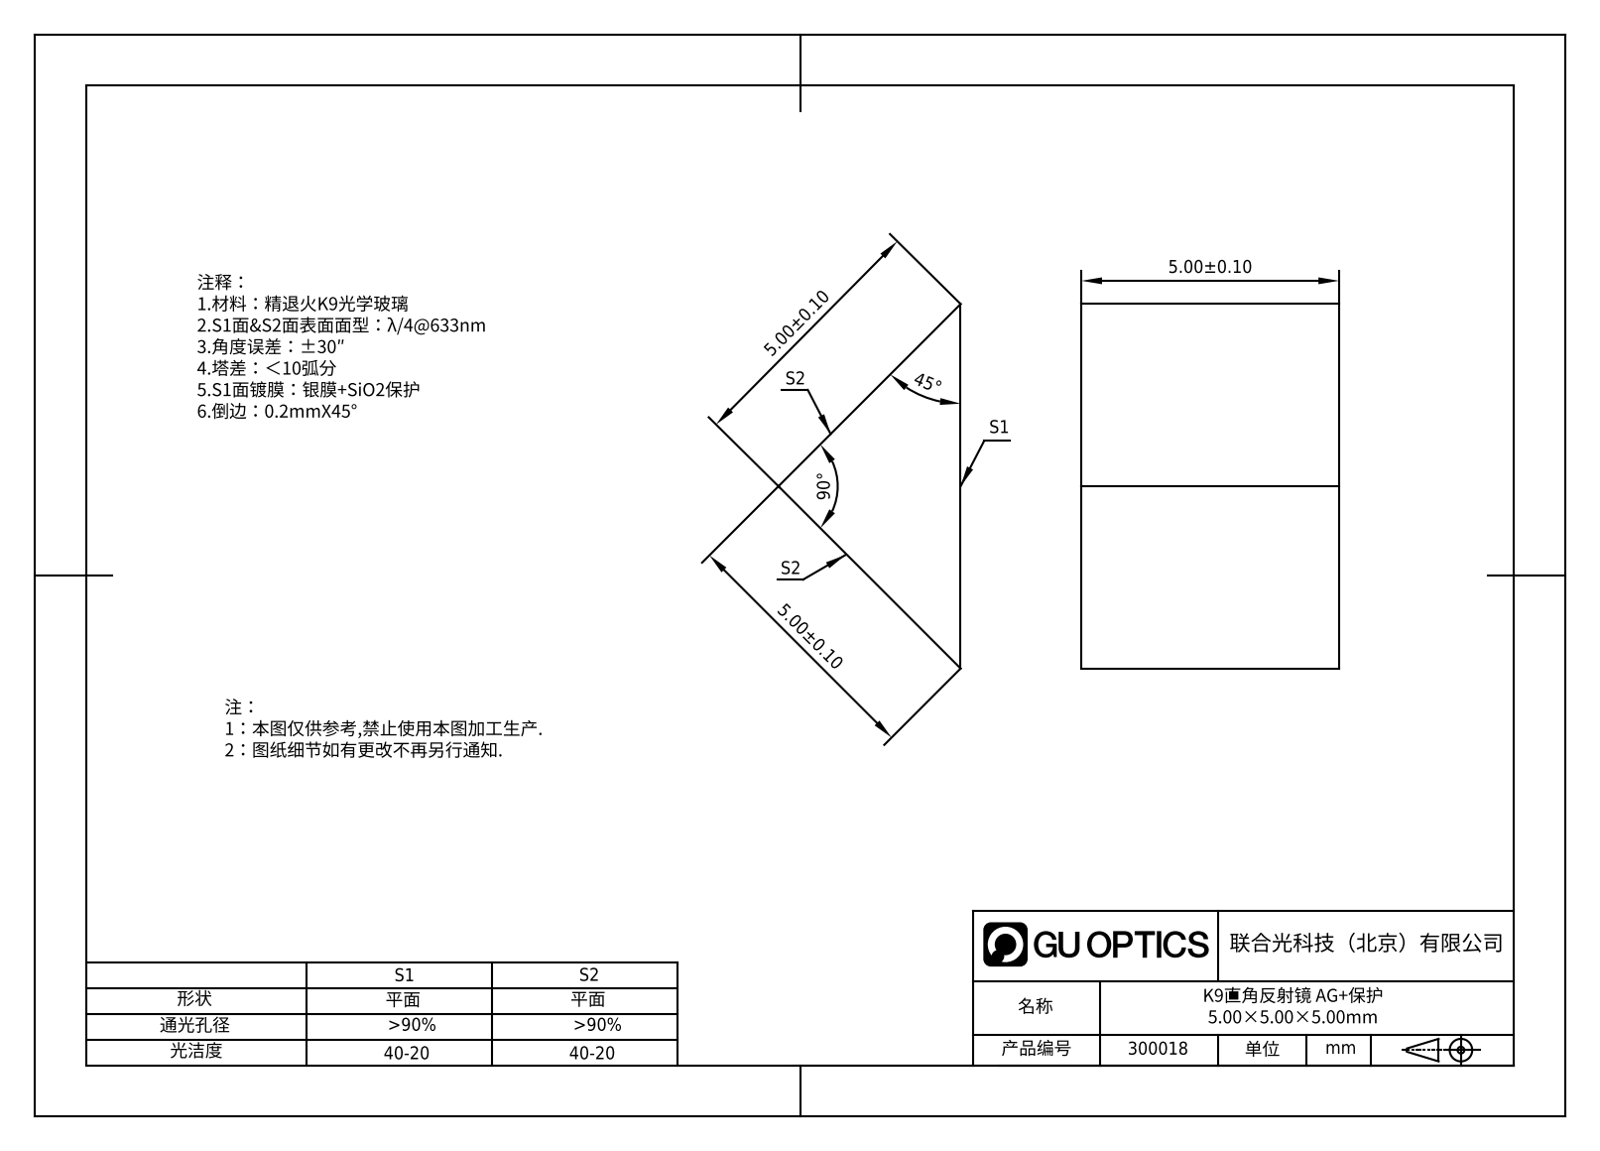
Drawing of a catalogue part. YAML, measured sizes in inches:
part_name: "300000"
step_written_by: "SolidWorks 2016 (AUTOMOTIVE_DESIGN)"
units: inches
bodies: {solids: 1, faces: 5, planar: 5, cylindrical: 0, other: 0}
overall_size: [0.278, 0.197, 0.139]
volume: 0.004
surface_area: 0.171
face_to_face_distances: [0.197]
